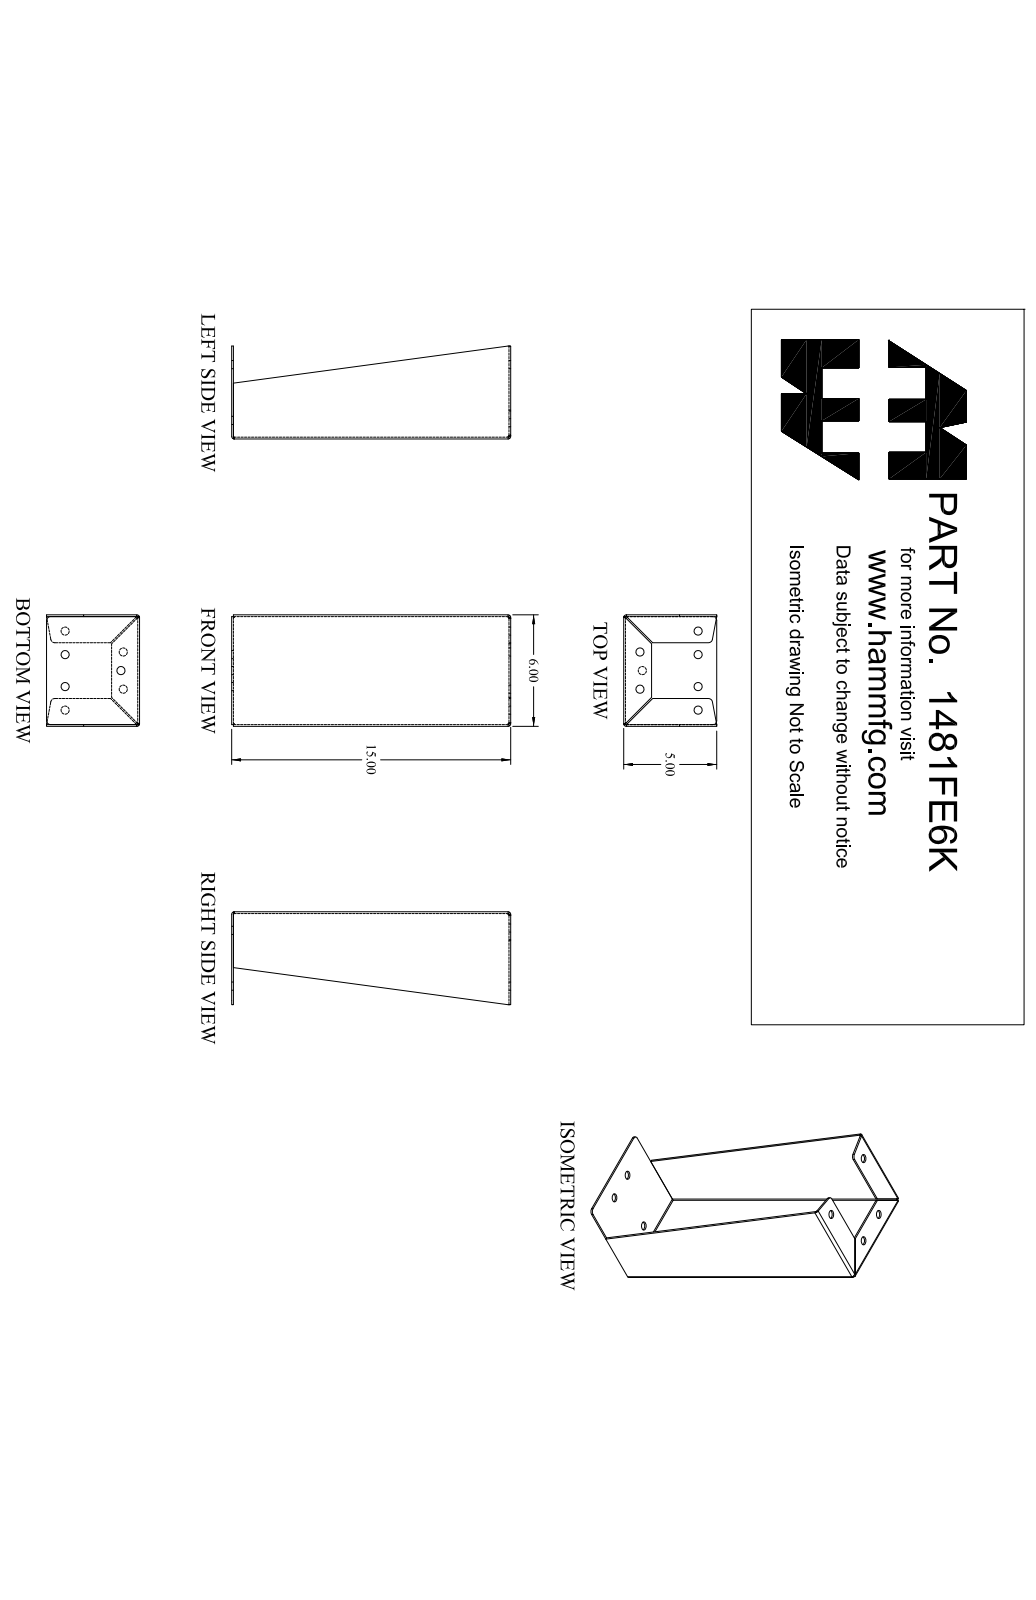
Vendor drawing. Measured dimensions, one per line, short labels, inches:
name: 1481FE6K_Default
written by: SolidWorks 2019 (CONFIG_CONTROL_DESIGN)
unit: in
bodies: 1 solid, 78 faces (42 planar, 30 cylindrical, 6 other)
size: 15 × 6 × 5
volume: 23.68 in³; area: 506.3 in²
holes: 7× ⌀0.437
rounds: 6× R0.048, 6× R0.143, 4× R0.22
face distances: 0.095, 5.905, 5.81, 6, 0.095, 14.81, 14.905, 14.905, 15, 1.405
hole spacings: 1.008, 3.12, 3.128, 3.321, 3.636, 4.419, 1.266, 1.266
